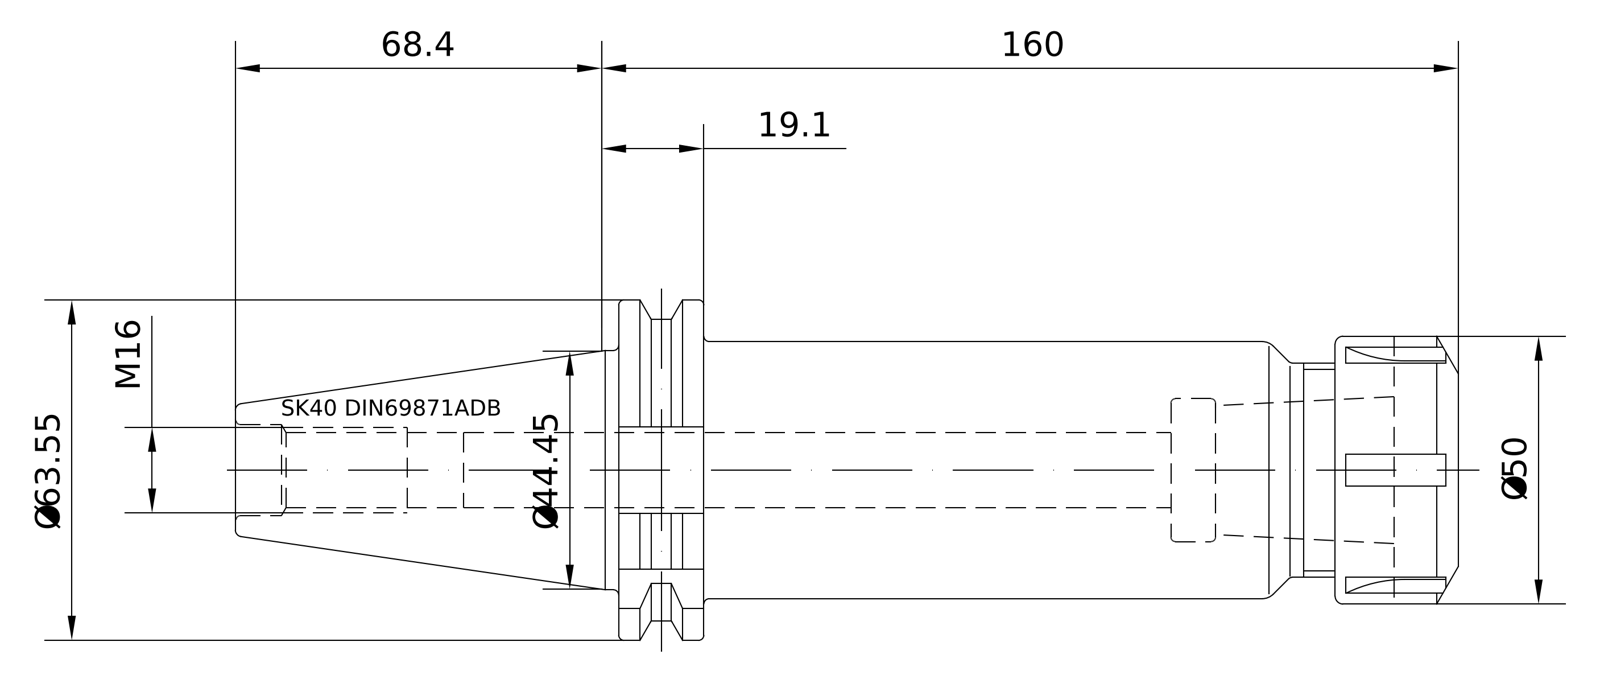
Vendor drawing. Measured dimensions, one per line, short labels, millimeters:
name: 40-322-32; 83-912-32; 40-322-32_ASM
written by: PRO/ENGINEER BY PARAMETRIC TECHNOLOGY CORPORATION, 2010430 (CONFIG_CONTROL_DESIGN)
unit: mm
bodies: 2 solids, 150 faces (50 planar, 37 cylindrical, 63 other)
size: 228.25 × 63.52 × 61.42
volume: 338 483 mm³; area: 49 646 mm²
holes: 1× ⌀13.84, 1× ⌀17.01, 1× ⌀17.5, 1× ⌀23.5
bosses: 1× ⌀50, 1× ⌀48, 1× ⌀47.5, 1× ⌀43.75, 1× ⌀40, 1× ⌀16.01
rounds: 6× R2.7, 1× R1.35, 1× R28, 1× R31.76
face distances: 134.3, 156.8, 22.5, 15.85, 118.45, 140.95, 143.8, 127.95, 9.5, 13
